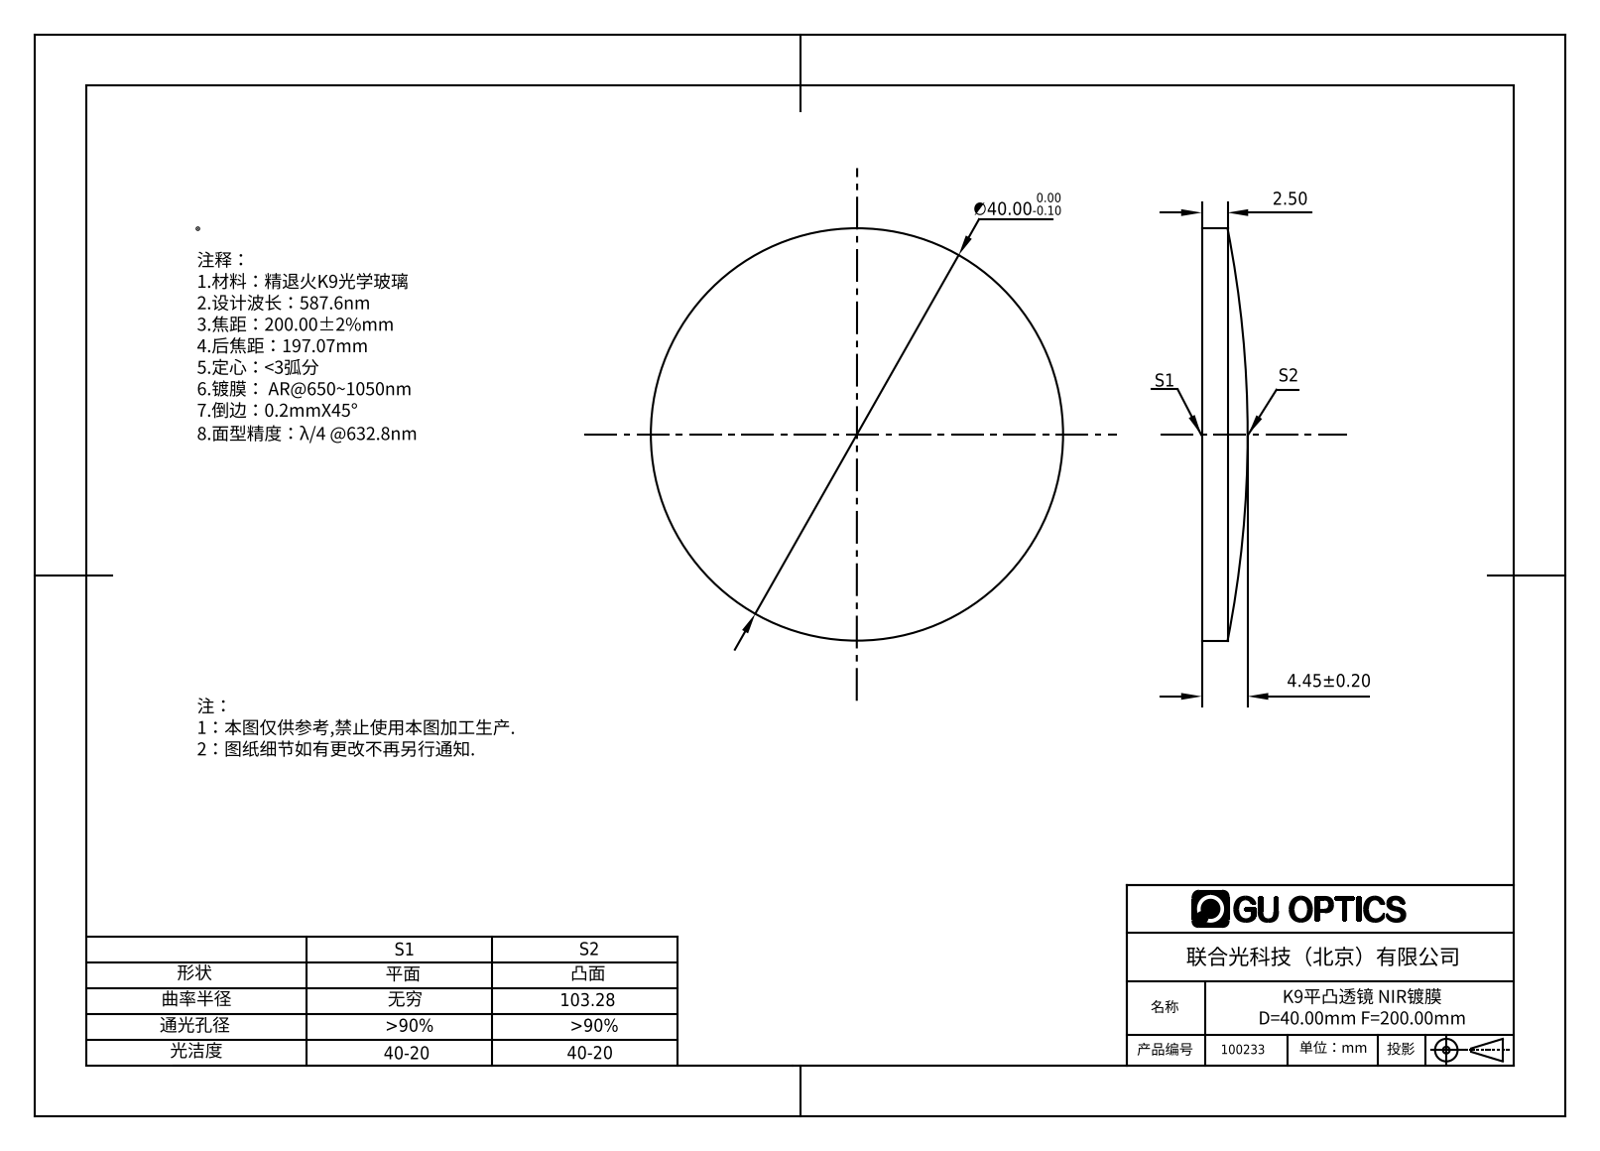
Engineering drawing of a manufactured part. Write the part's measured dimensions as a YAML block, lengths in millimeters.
part_name: "100233"
step_written_by: "SolidWorks 2016 (AUTOMOTIVE_DESIGN)"
units: millimeters
bodies: {solids: 1, faces: 5, planar: 1, cylindrical: 2, other: 2}
overall_size: [40, 40, 4.45]
volume: 4371
surface_area: 2839
round_bosses_or_shafts:
  - {diameter: 40, count: 1}
